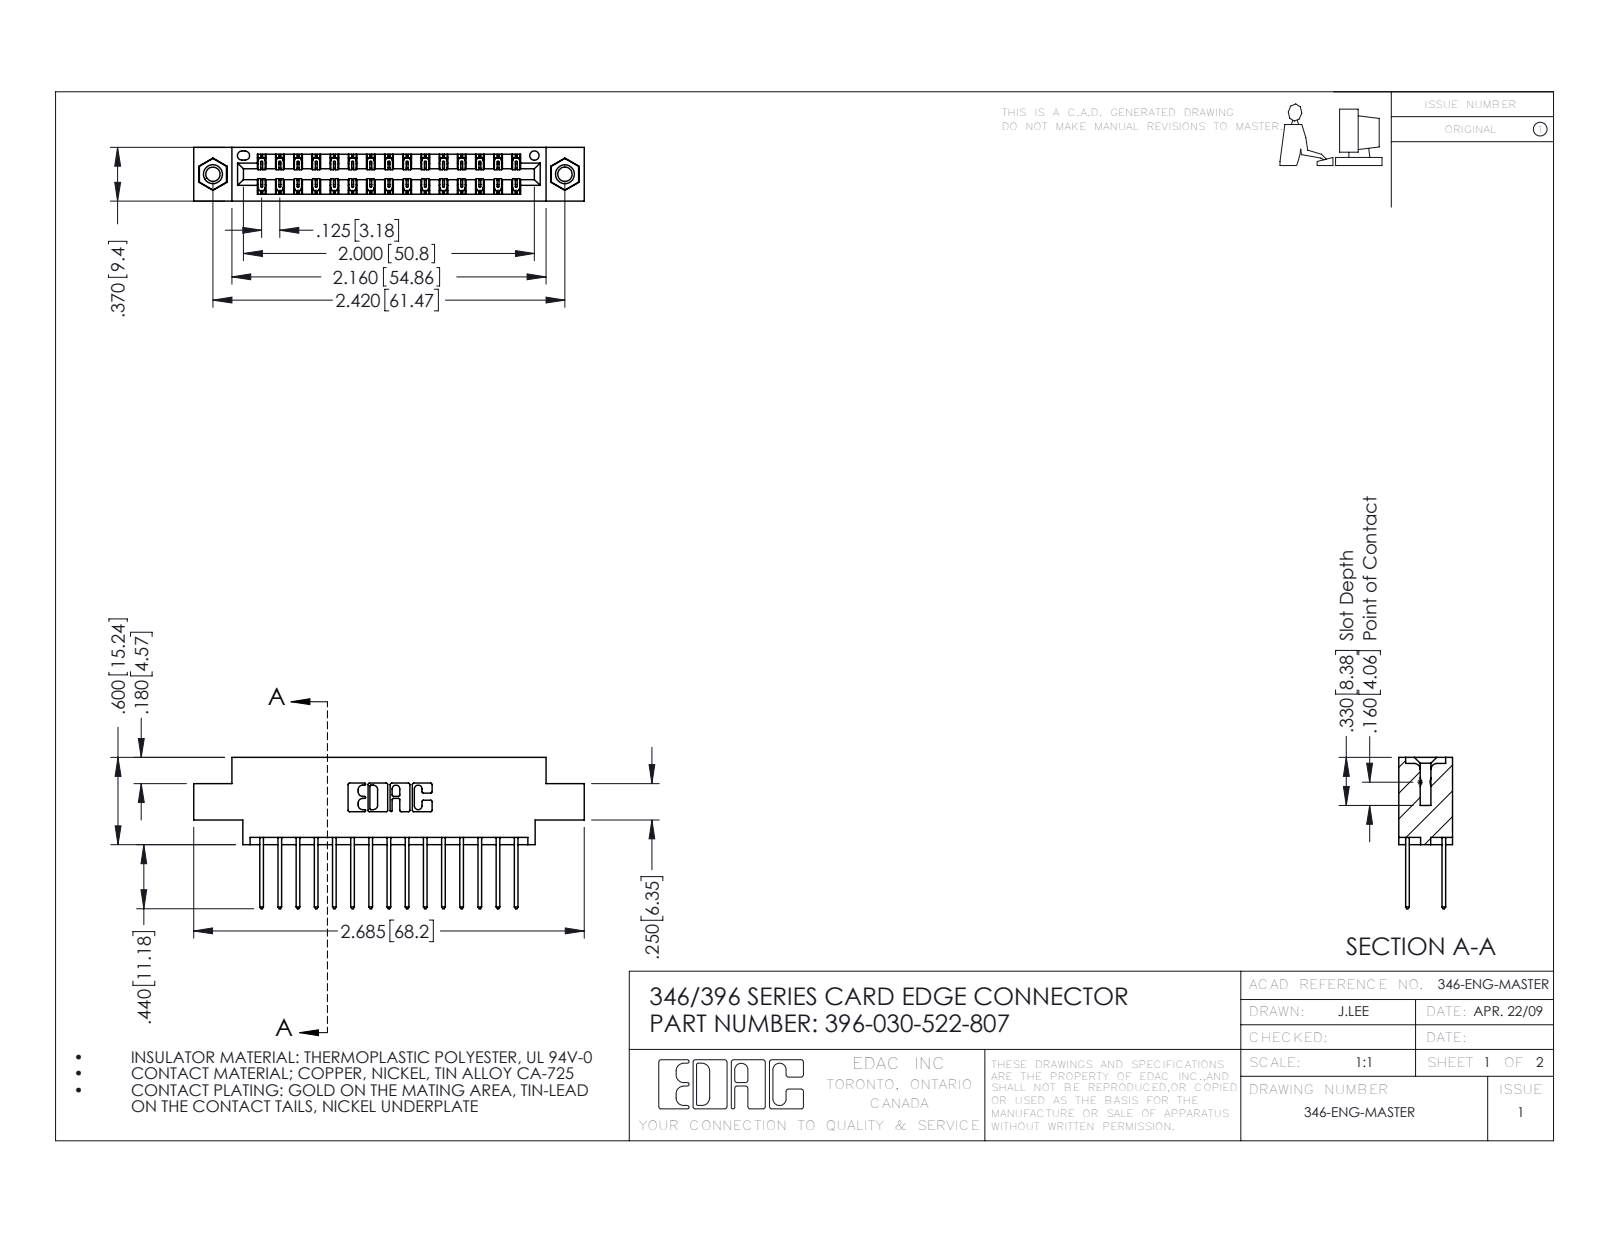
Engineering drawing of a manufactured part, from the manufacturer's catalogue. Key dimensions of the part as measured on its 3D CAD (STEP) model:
Part name (STEP PRODUCT): 345-250-001_345-250-005-103; 396-030-522-807; 345-292-001_345-293-122; 346 Part_0.170 Offset - 0.156 Dia-TI
STEP written by: SolidWorks 2016 (CONFIG_CONTROL_DESIGN)
Units: inches
Bodies: 33 solids, 1746 faces (1162 planar, 568 cylindrical, 16 other)
Overall size (bounding box): 2.685 × 1.04 × 0.37
Volume: 0.387 in³ · Surface area: 13.75 in²
Round holes (diameter × count): ⌀0.098 ×2, ⌀0.125 ×2, ⌀0.156 ×2, ⌀0.064 ×1
Round bosses / shafts (diameter × count): ⌀0.155 ×2
Partial cylindrical surfaces — rounded edges, fillets, slot ends (radius × count): R0.006 ×45, R0.01 ×30, R0.01 ×22, R0.007 ×6, R0.031 ×6, R0.026 ×3, R0.014 ×2, R0.022 ×2
Main face-to-face distances: 0.048, 0.322, 0.25, 0.37, 0.072, 0.298, 0.025, 0.275, 0.222, 0.148
Hole centre spacings: 0.246, 2.213, 2.42
